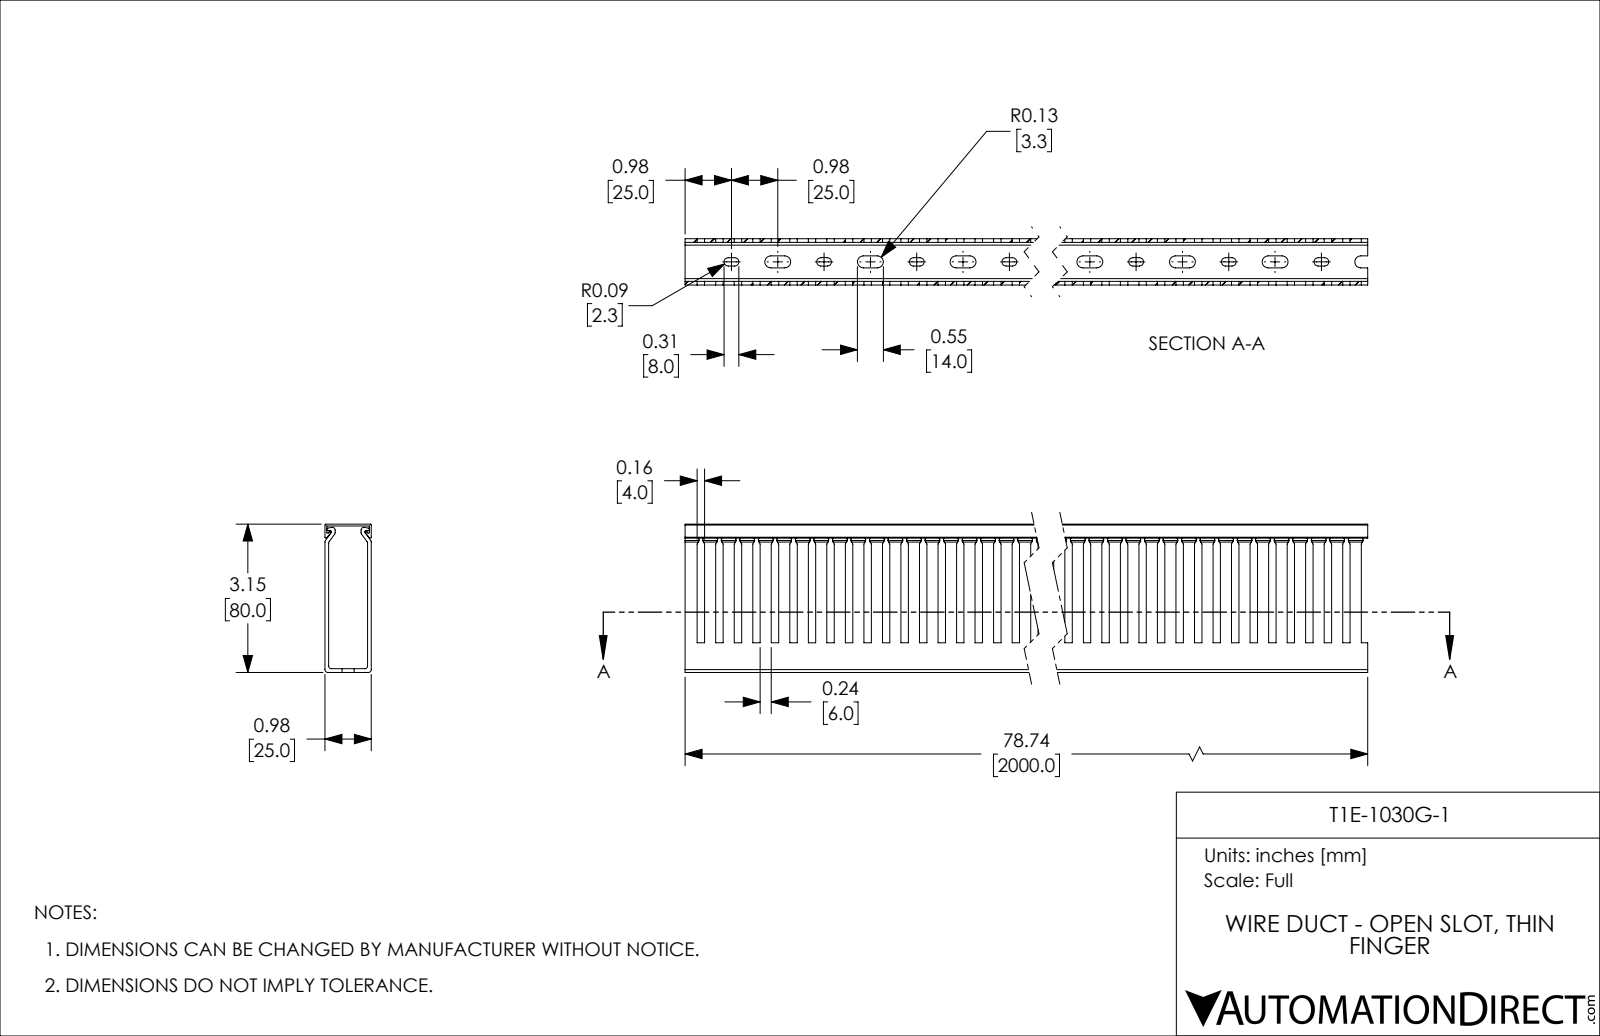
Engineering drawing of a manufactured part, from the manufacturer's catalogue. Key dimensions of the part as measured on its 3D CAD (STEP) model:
Part name (STEP PRODUCT): T1E-1030W-1
STEP written by: SolidWorks 2021 (CONFIG_CONTROL_DESIGN)
Units: millimetres
Bodies: 2 solids, 945 faces (514 planar, 431 cylindrical, 0 other)
Overall size (bounding box): 2000 × 80 × 25
Volume: 801 529 mm³ · Surface area: 894 454 mm²
Partial cylindrical surfaces — rounded edges, fillets, slot ends (radius × count): R2.25 ×80, R3.25 ×80, R1.5 ×12, R0.5 ×8, R0.75 ×6
Main face-to-face distances: 2, 23, 25, 21, 1, 80, 79, 77, 78, 24
